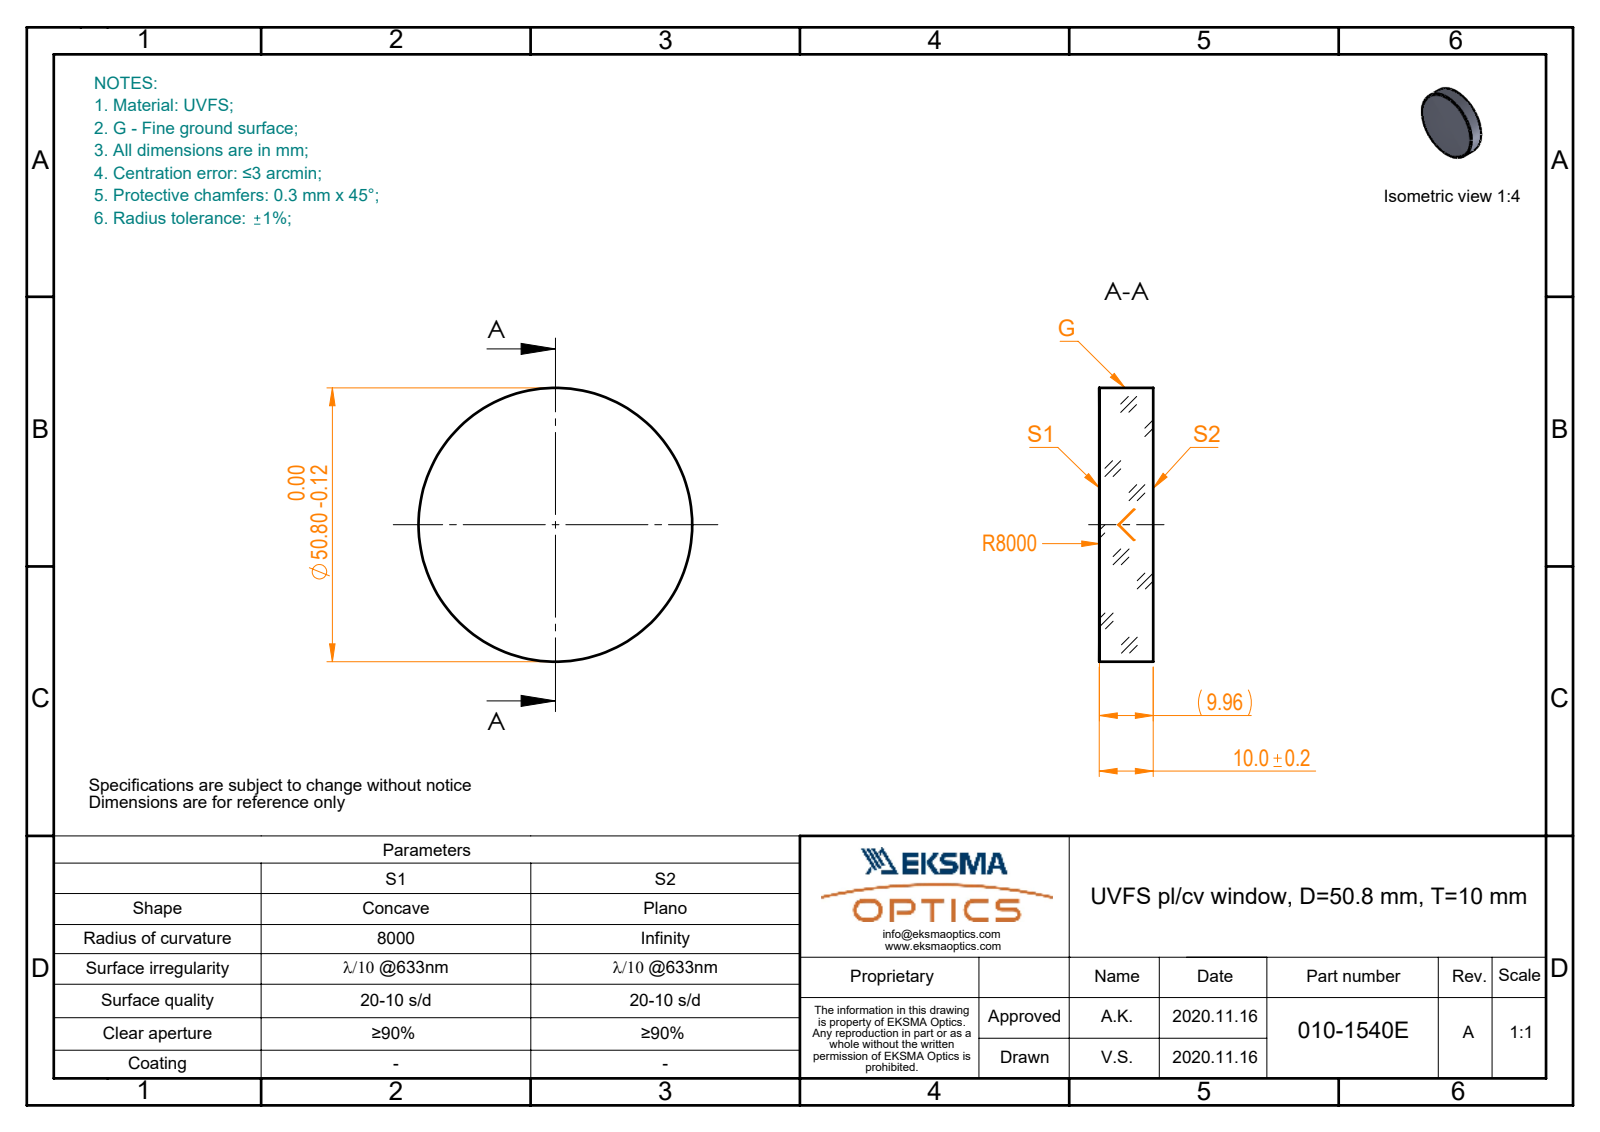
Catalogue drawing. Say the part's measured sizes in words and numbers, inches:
The part is named "010-1540E_UVFS_PCV_window". Its 3-D file was written by "SolidWorks 2019 (CONFIG_CONTROL_DESIGN)". It is 1 solid with 5 faces: 1 planar, 2 cylindrical and 2 other. Overall it measures 2 by 2 by 0.394 inches. Its volume is 1.234 cubic inches and its surface area 8.758 square inches. Round bosses or shafts: 1 of diameter 2.
